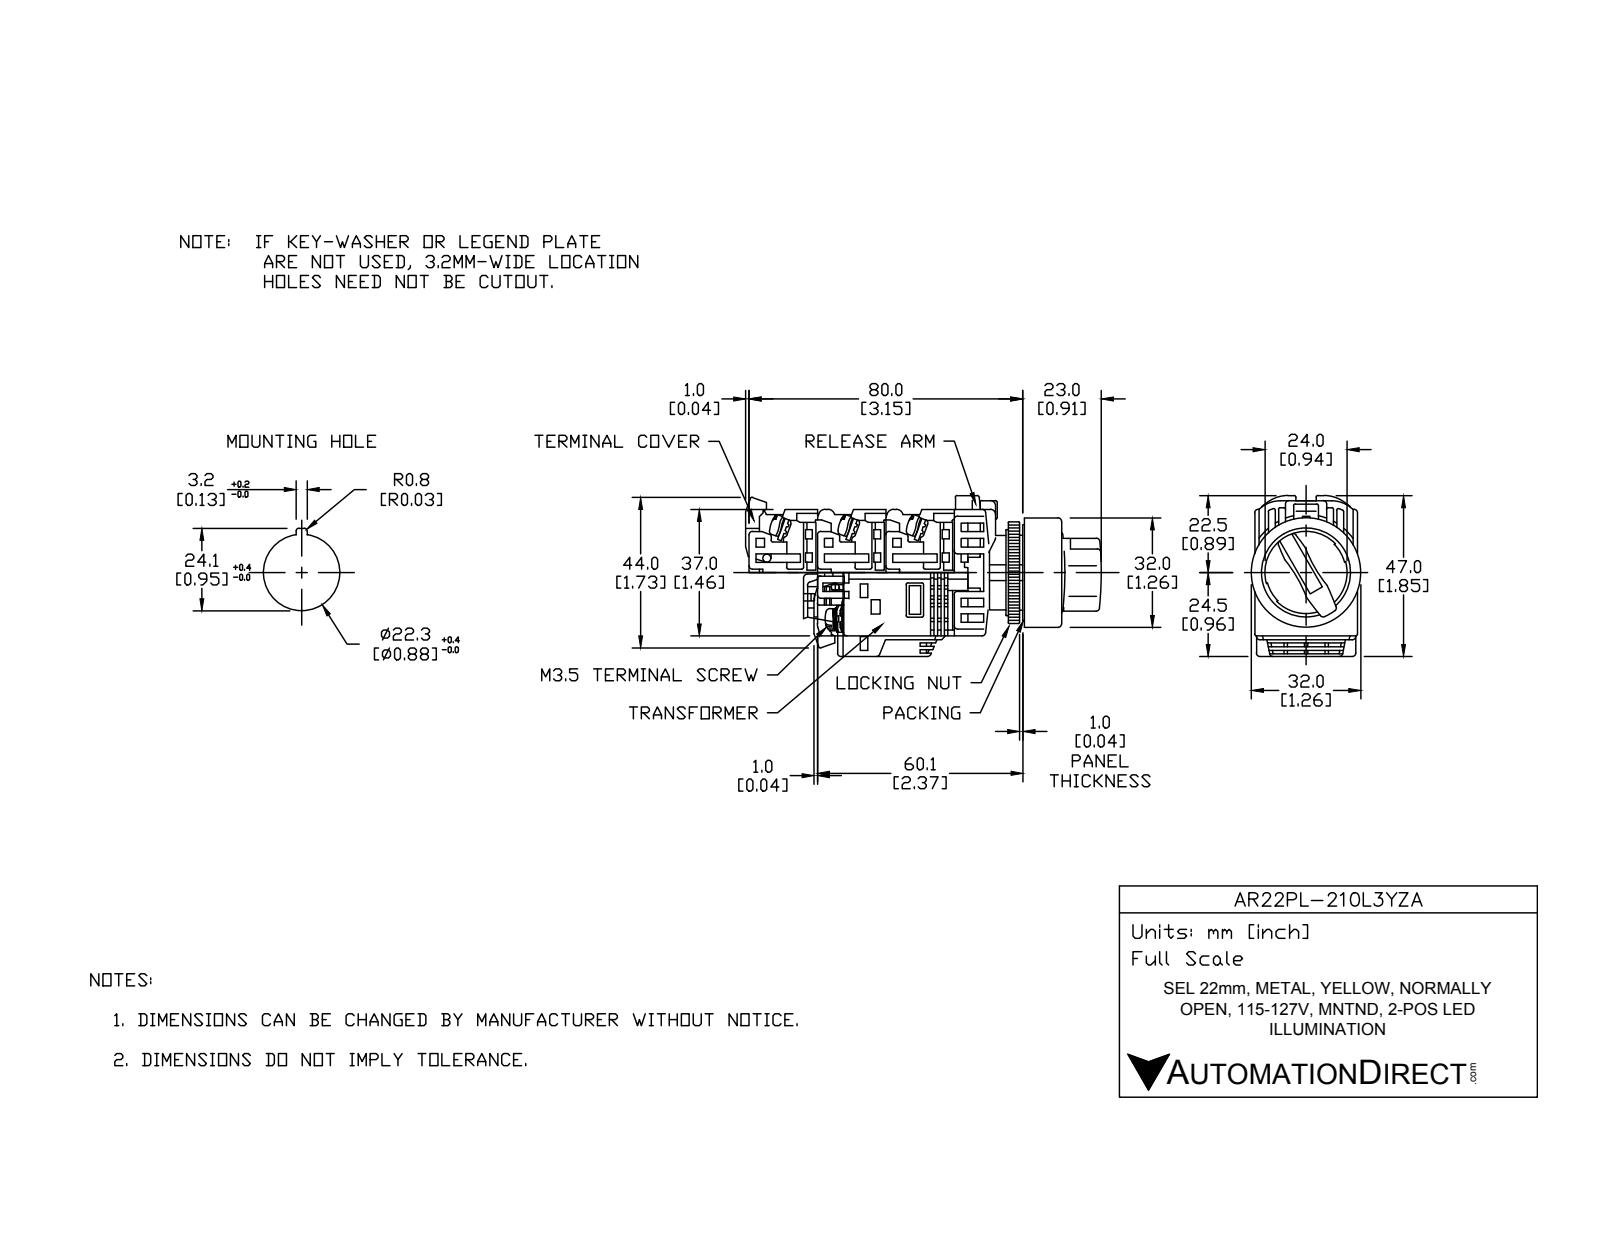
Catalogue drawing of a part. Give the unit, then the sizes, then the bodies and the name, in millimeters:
Units: millimetres
Overall size (bounding box): 84.5 × 43.81 × 32
Round holes (diameter × count): ⌀21.8 ×1, ⌀22 ×1, ⌀25 ×1, ⌀31 ×1
Round bosses / shafts (diameter × count): ⌀5 ×4, ⌀32 ×1, ⌀30.5 ×1, ⌀29.8 ×1, ⌀24 ×1, ⌀21.75 ×1, ⌀17 ×1
Partial cylindrical surfaces — rounded edges, fillets, slot ends (radius × count): R0.5 ×39, R1.75 ×8, R1 ×6, R5 ×4, R4 ×2, R12 ×1, R16.59 ×1, R17.59 ×1
Main face-to-face distances: 1, 18, 29, 20, 3, 28.5, 0.5, 2, 21, 10
Volume: 48 971 mm³ · Surface area: 26 711 mm²
Bodies: 18 solids, 462 faces (317 planar, 118 cylindrical, 27 other)
Part name (STEP PRODUCT): AR22PL-210L3YZA
STEP written by: SolidWorks 2017 (AUTOMOTIVE_DESIGN)
